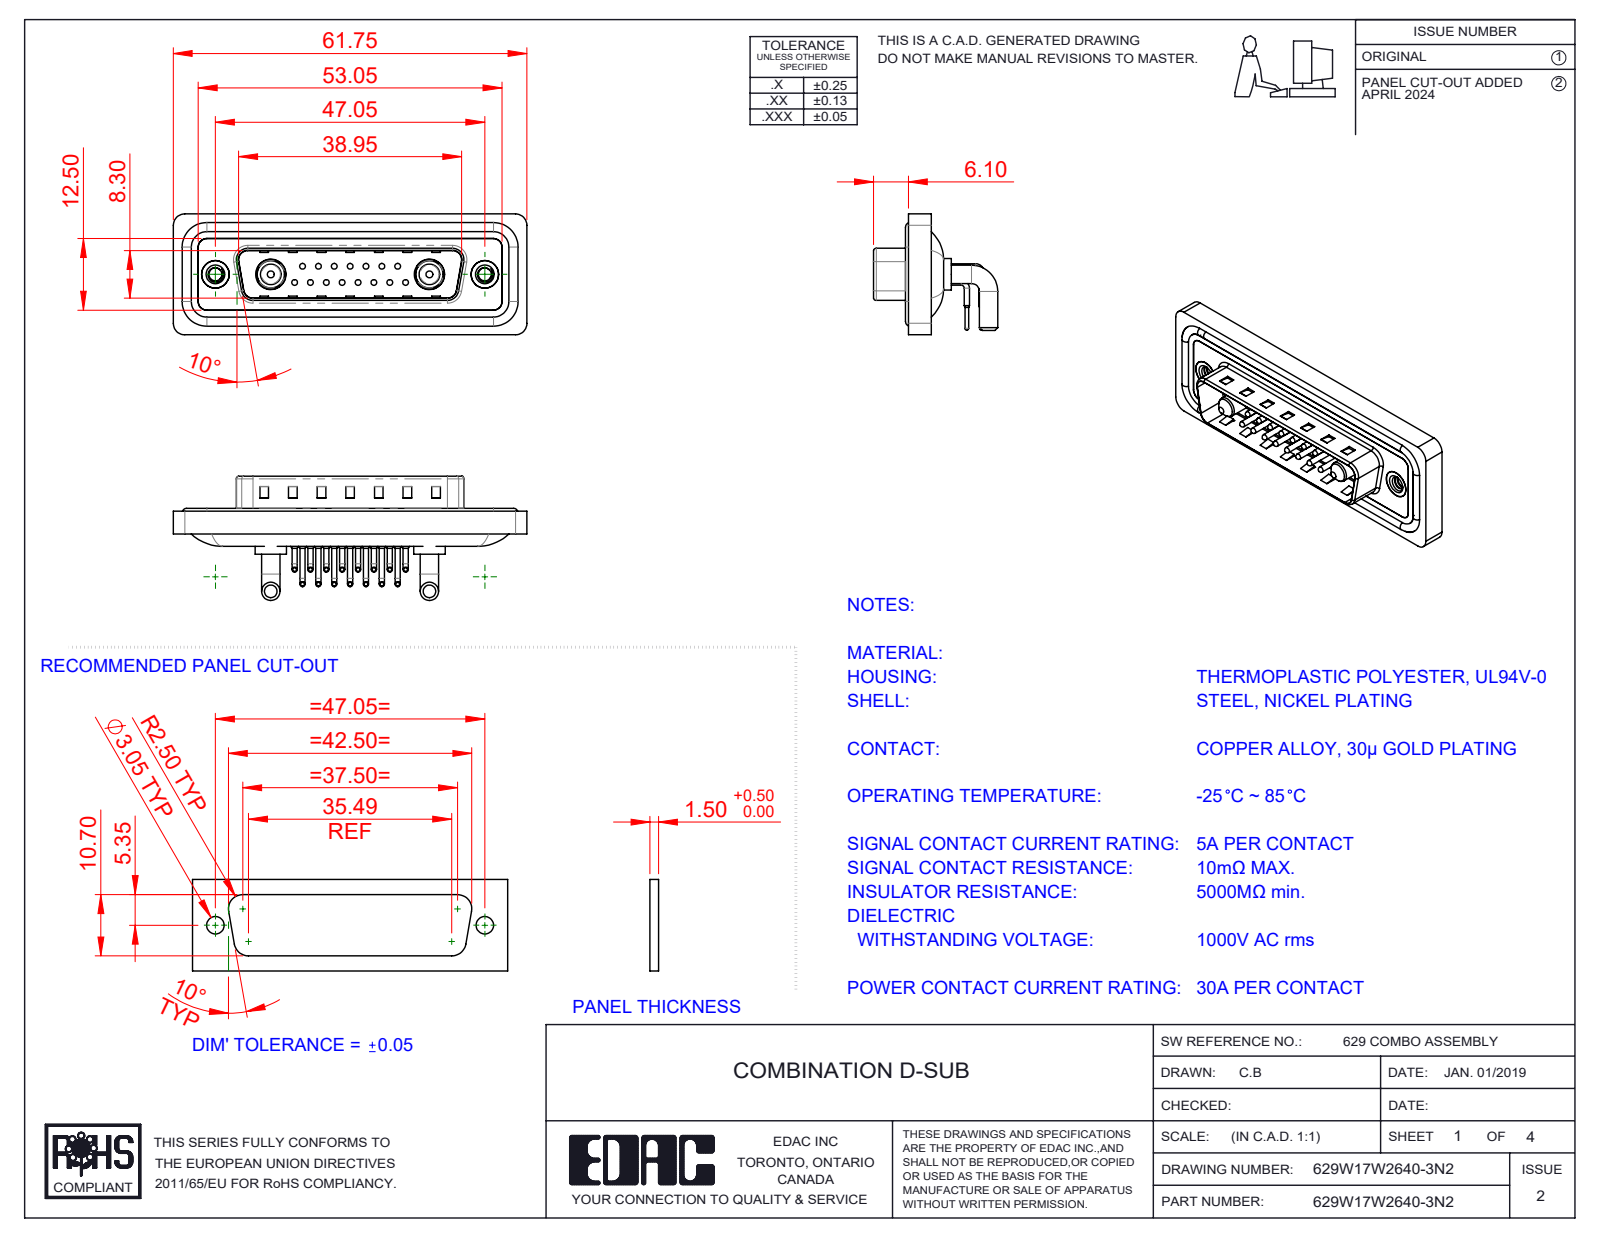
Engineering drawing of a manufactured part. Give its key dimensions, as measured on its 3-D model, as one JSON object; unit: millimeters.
{"part_name": "629Combo Waterproof Housing_25 Contacts; 629Combo Shell Front_25 Contacts; Power Pin_30A RA; 629Combo Shell Rear_25 Contacts (+5 more)", "step_written_by": "SolidWorks 2023 (CONFIG_CONTROL_DESIGN)", "units": "millimeters", "bodies": {"solids": 26, "faces": 2219, "planar": 1189, "cylindrical": 770, "other": 260}, "overall_size": [61.75, 21.7, 21.1], "volume_mm3": 7579, "surface_area_mm2": 12638, "round_holes": [[0.75, 15], [1.6, 15], [2, 15], [2.26, 2], [4, 2], [4.8, 2], [4.85, 2], [5, 2], [5.3, 2]], "round_bosses_or_shafts": [[0.9, 30], [1.5, 15], [1, 15], [0.65, 15], [3.2, 4], [1.6, 4], [5.5, 2], [5.2, 2]], "partial_cylinders_radius": [[1.5, 18], [2, 18], [1.01, 15], [0.5, 8], [1.6, 8], [0.25, 4], [0.6, 4], [0.65, 4]], "face_to_face_distances": [0.4, 2.9, 0.8, 4.1, 1.1, 2.1, 1.6, 4.5, 1.5, 2.5], "hole_center_spacings": [3.16, 2.77, 5.54, 8.31, 5.04, 7.49, 11.08, 5.03]}
